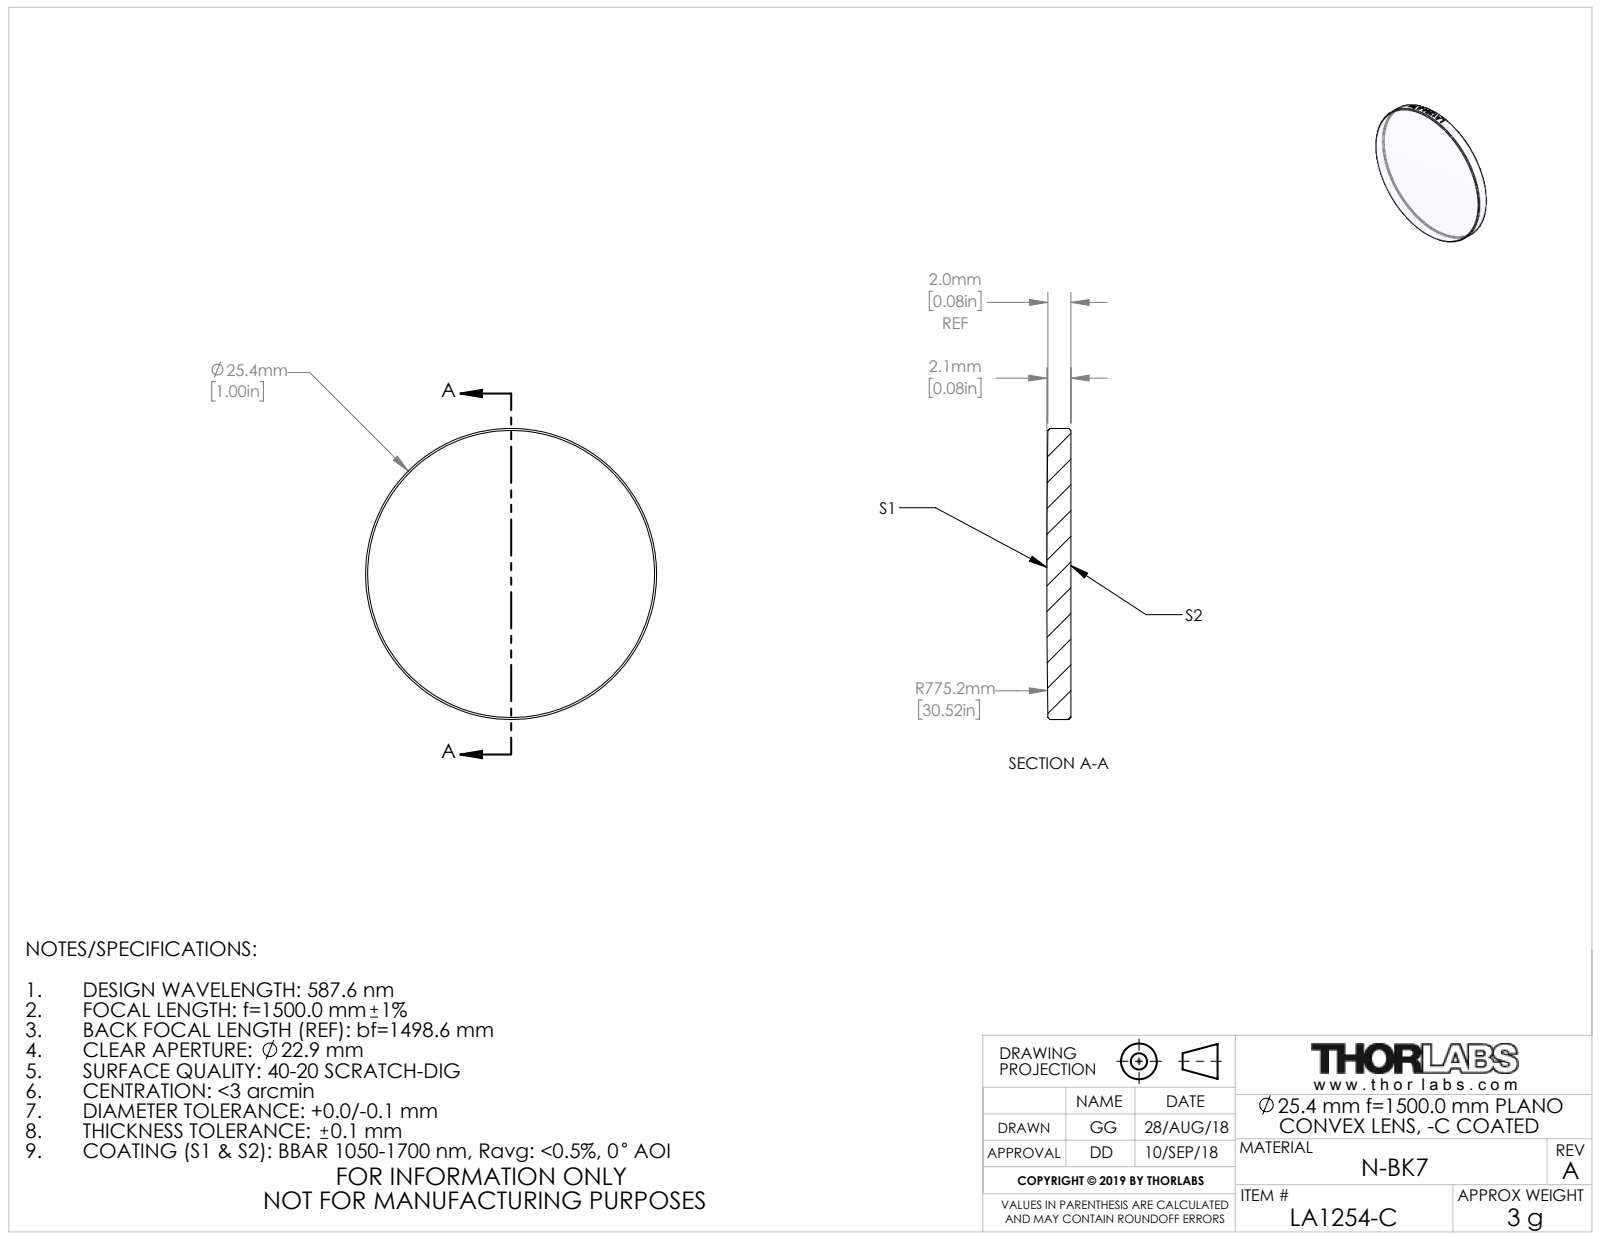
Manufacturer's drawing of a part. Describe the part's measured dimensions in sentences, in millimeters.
The part is named "TTN162125-E0W". Its 3-D file was written by "SolidWorks 2018 (CONFIG_CONTROL_DESIGN)". It is 1 solid with 25 faces: 1 planar, 18 cylindrical and 6 other. Overall it measures 25.4 by 25.4 by 2.1 millimeters. Its volume is 1 035 cubic millimeters and its surface area 1 156 square millimeters. Round bosses or shafts: 1 of diameter 25.4.
